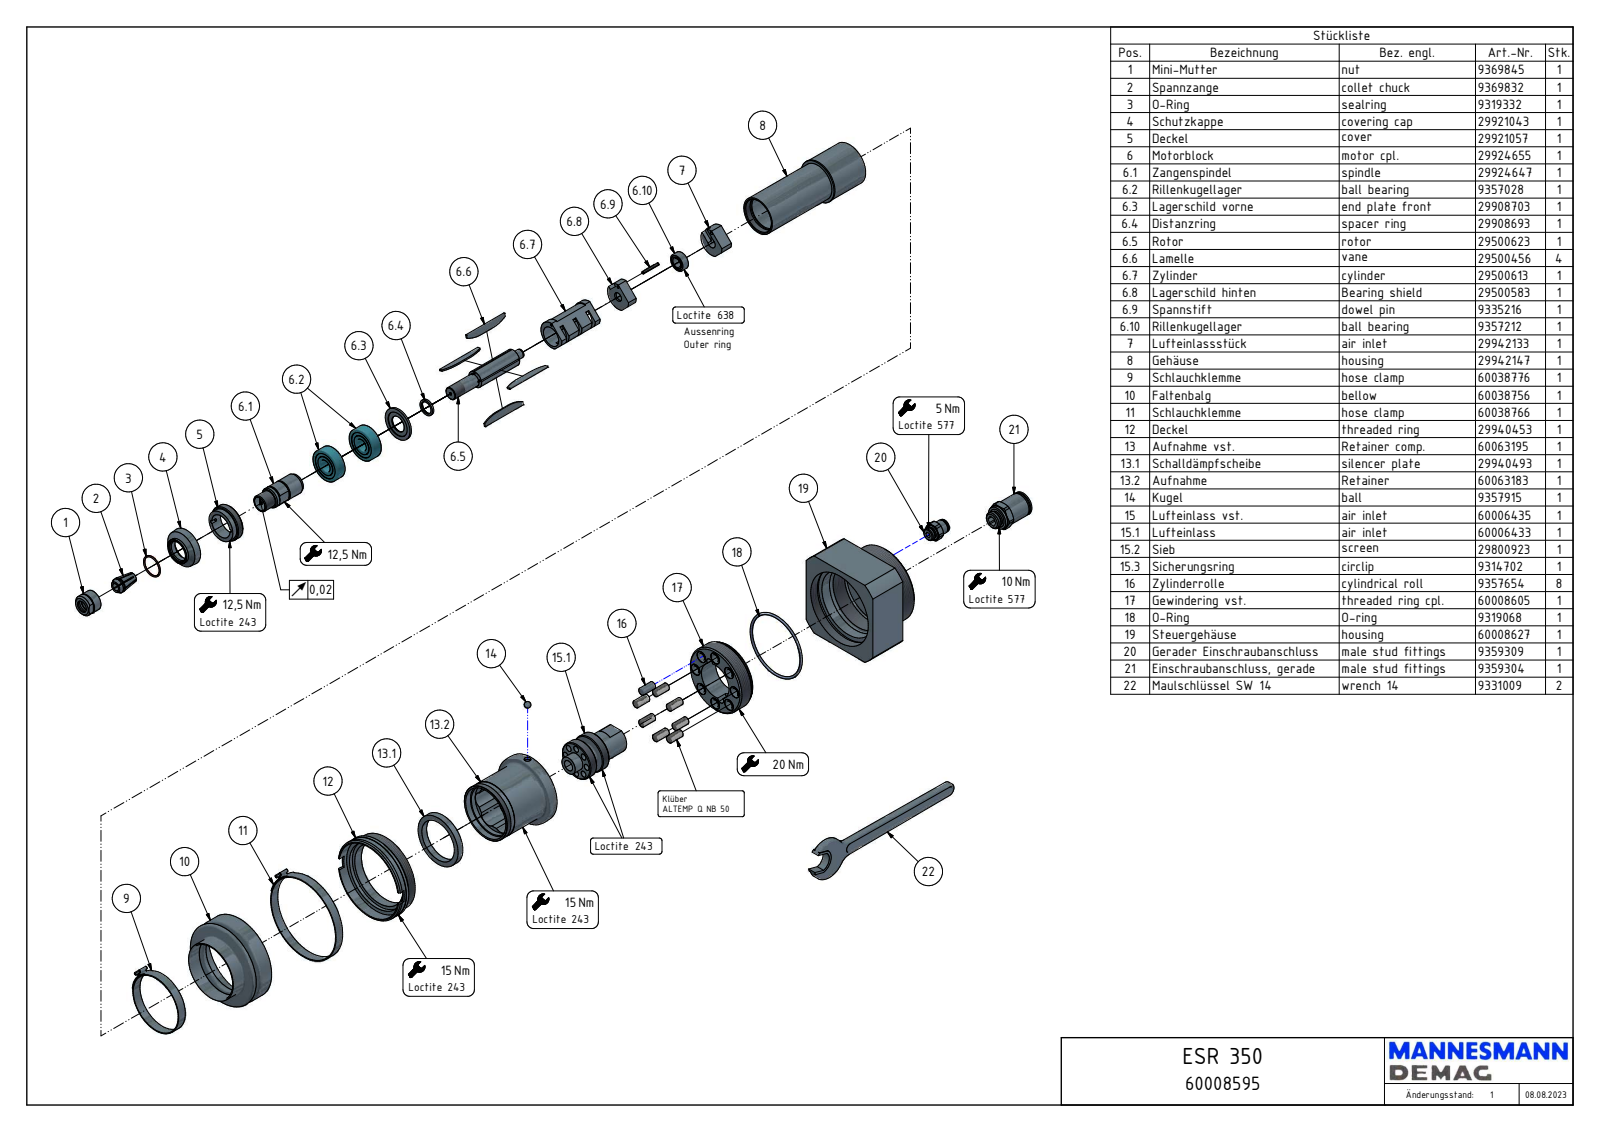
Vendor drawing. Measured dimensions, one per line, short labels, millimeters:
name: ESR 350_60008595
written by: Autodesk Inventor 2024 (AUTOMOTIVE_DESIGN)
unit: mm
bodies: 1 solid, 342 faces (140 planar, 117 cylindrical, 85 other)
size: 198.52 × 70 × 70
volume: 343 141 mm³; area: 45 791 mm²
holes: 4× ⌀4.13, 2× ⌀4.99, 2× ⌀5, 2× ⌀6, 1× ⌀1, 1× ⌀7, 1× ⌀8.57, 1× ⌀9.19, 1× ⌀9.2, 1× ⌀12, 1× ⌀12.19, 1× ⌀13
bosses: 1× ⌀68.7, 1× ⌀67.5, 1× ⌀62, 1× ⌀60, 1× ⌀48.2, 1× ⌀47, 1× ⌀45, 1× ⌀34.5
rounds: 8× R0.5, 8× R1, 8× R1.1, 8× R19, 4× R1.4, 4× R2, 1× R7, 1× R24.11
face distances: 70, 17, 31.5, 48.5, 63, 80, 77.74, 46.24, 14.74, 2.26
hole spacings: 10.5, 47.18, 21, 46, 50.57
